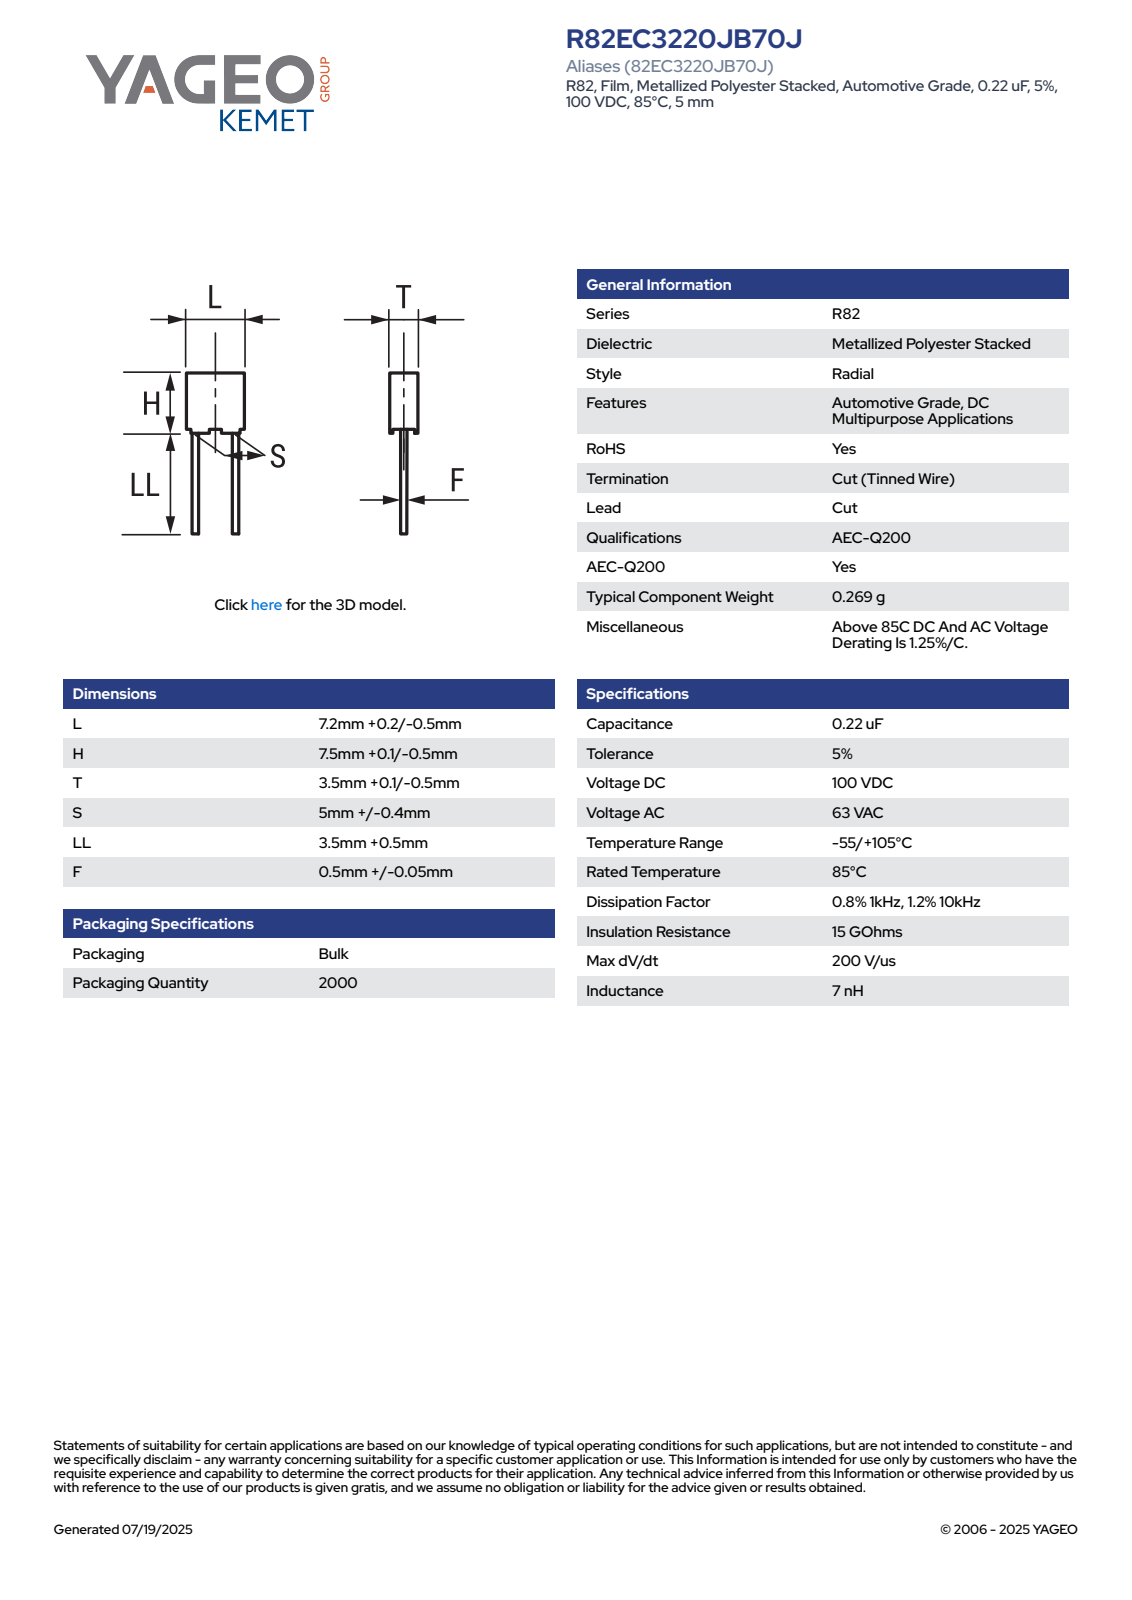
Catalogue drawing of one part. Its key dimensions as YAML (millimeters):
part_name: "CFR_RB3_7.2X7.5X3.5_L7.4H7.6T3.6S5LL4F0.55"
step_written_by: "SolidWorks 2014 (AUTOMOTIVE_DESIGN)"
units: millimeters
bodies: {solids: 4, faces: 85, planar: 77, cylindrical: 8, other: 0}
overall_size: [11.6, 7.4, 3.6]
volume: 187
surface_area: 249
round_bosses_or_shafts:
  - {diameter: 0.55, count: 2}
partial_cylinders:
  - {radius: 0.5, count: 4}
face_to_face_distances: [3.6, 7.4, 6.85, 3.35, 3.1, 7.15, 0.75, 7.6, 6.9, 0.49]
